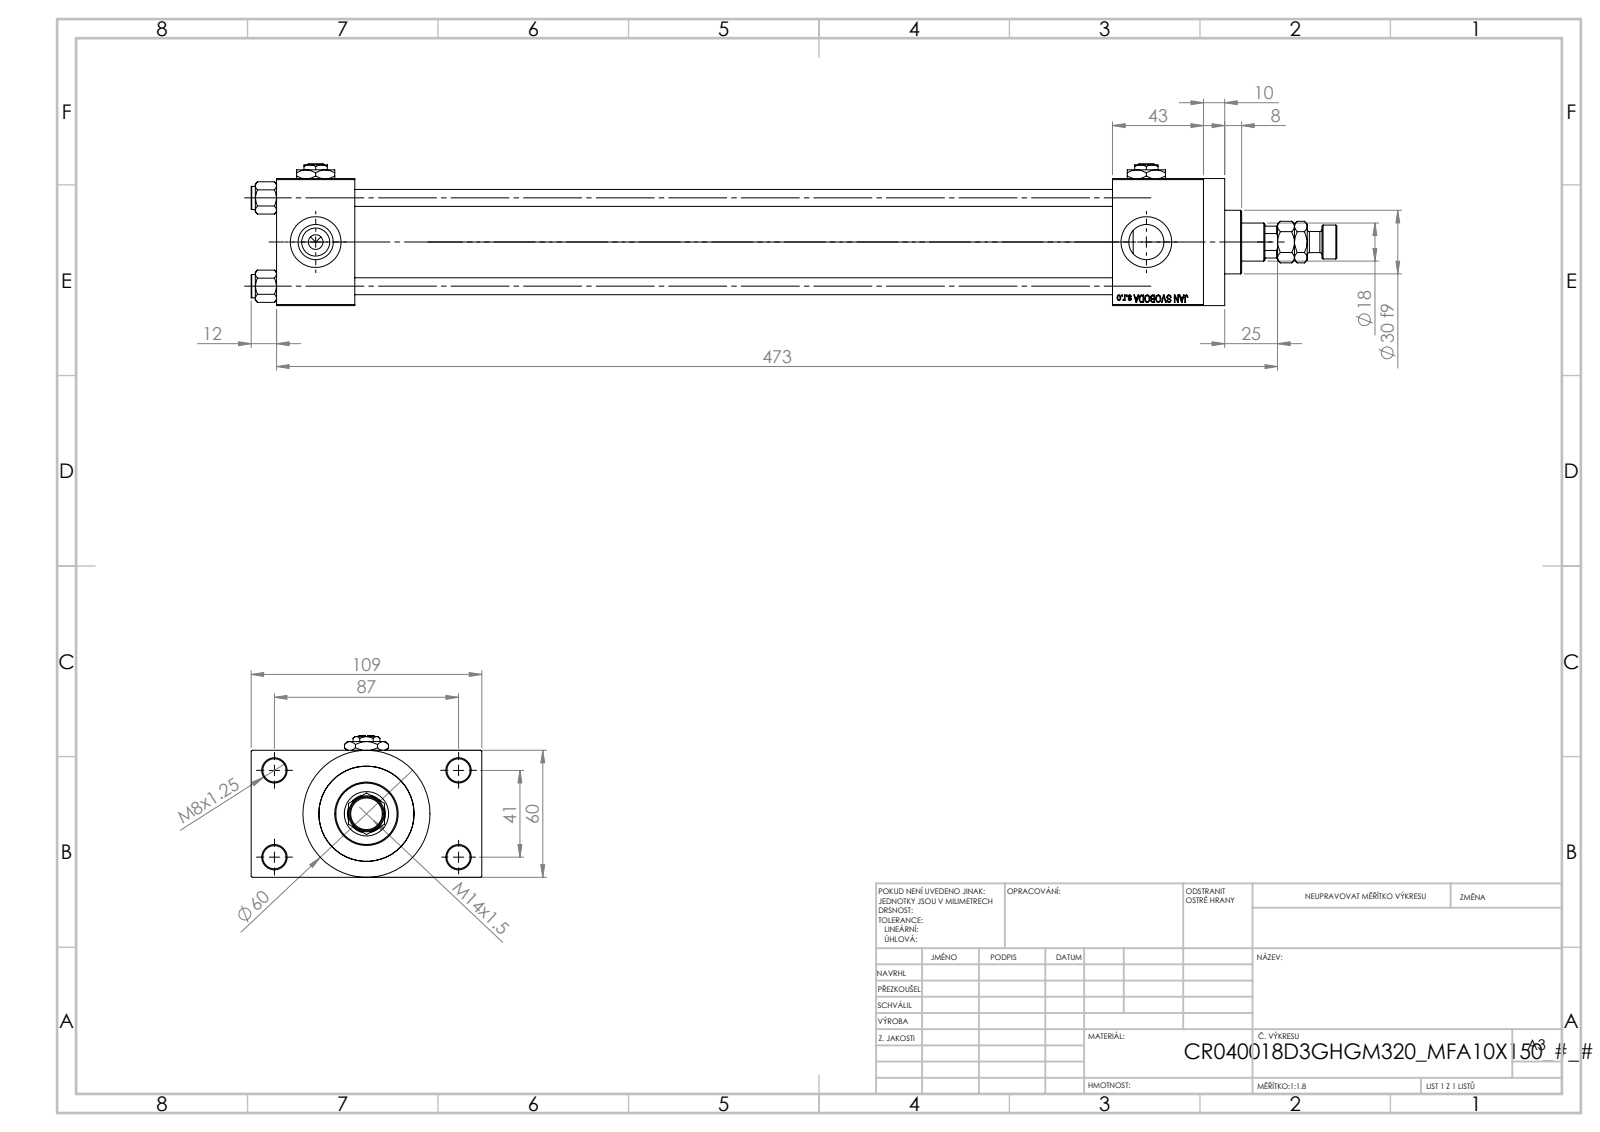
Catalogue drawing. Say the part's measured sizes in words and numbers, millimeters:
The part is named "MFA; NUT_M5_D; Zatka_pro_OIL_PORT; V215CR_D_TYCINKA (+3 more)". Its 3-D file was written by "SolidWorks 2019 (CONFIG_CONTROL_DESIGN)". It is 14 solids with 1257 faces: 562 planar, 103 cylindrical and 592 other. Overall it measures 513 by 109 by 67 millimeters. Its volume is 774 002 cubic millimeters and its surface area 255 433 square millimeters. Round holes: 4 of diameter 8, 4 of diameter 11, 4 of diameter 16.66, 4 of diameter 24, 3 of diameter 7, 1 of diameter 8.5, 1 of diameter 18, 1 of diameter 21, 1 of diameter 31, 1 of diameter 40, 1 of diameter 45. Round bosses or shafts: 4 of diameter 11, 1 of diameter 60, 1 of diameter 46, 1 of diameter 30, 1 of diameter 16, 1 of diameter 10. Partial cylindrical surfaces (rounded edges, fillets, slot ends): 1 of radius 8.5. The main face-to-face distances are 60, 358, 24.5, 84.5, 37, 395, 43, 438, 401, 53. The hole center spacings are 22.65, 29.49, 41.7, 47.15, 48.09, 64.35, 76.49, 41.
